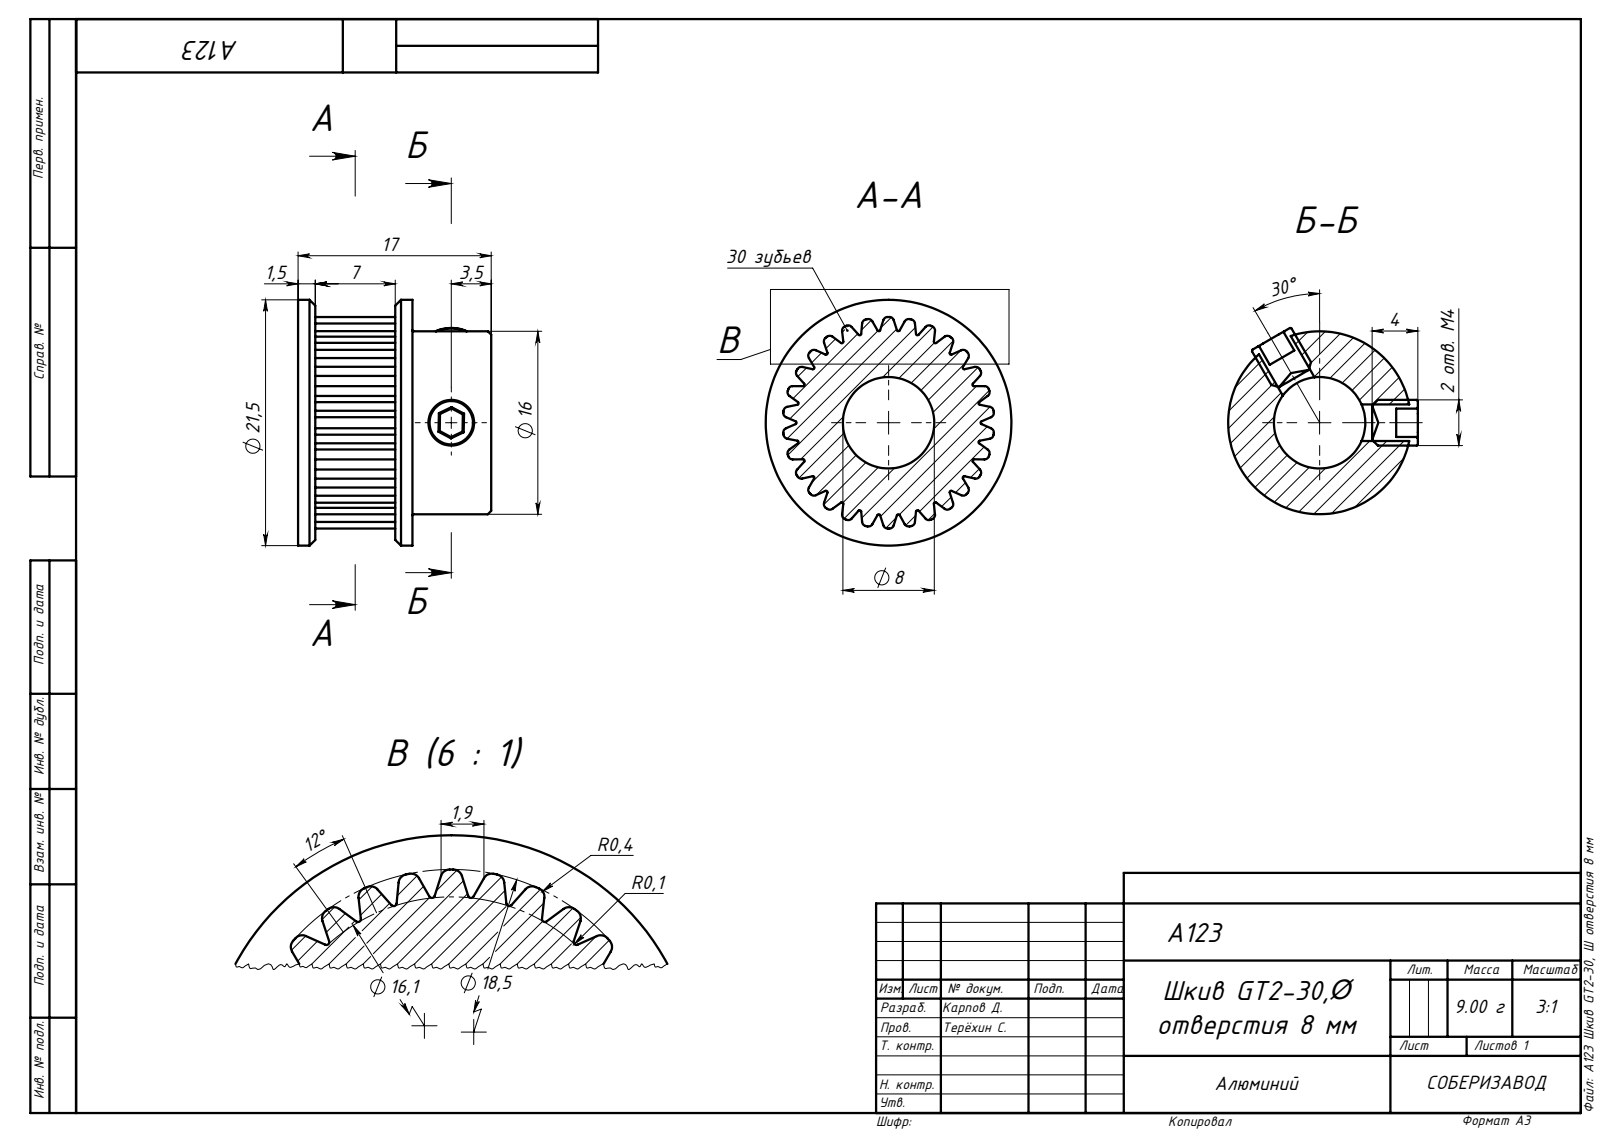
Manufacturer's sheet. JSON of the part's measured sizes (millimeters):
{"part_name": "A123 Шкив GT2-30, O отверстия 8 мм", "step_written_by": "SolidWorks 2019 (AUTOMOTIVE_DESIGN)", "units": "millimeters", "bodies": {"solids": 3, "faces": 281, "planar": 94, "cylindrical": 163, "other": 24}, "overall_size": [21.5, 21.5, 17], "volume_mm3": 3339, "surface_area_mm2": 2698, "round_holes": [[3.2, 2], [8, 1]], "round_bosses_or_shafts": [[4, 2], [21.5, 1], [16, 1]], "partial_cylinders_radius": [[0.4, 60], [0.13, 30], [9.25, 1]], "face_to_face_distances": [6.3, 1.5, 8.5, 10, 10.1, 6.9, 16.9, 17, 8.4, 8.6]}
